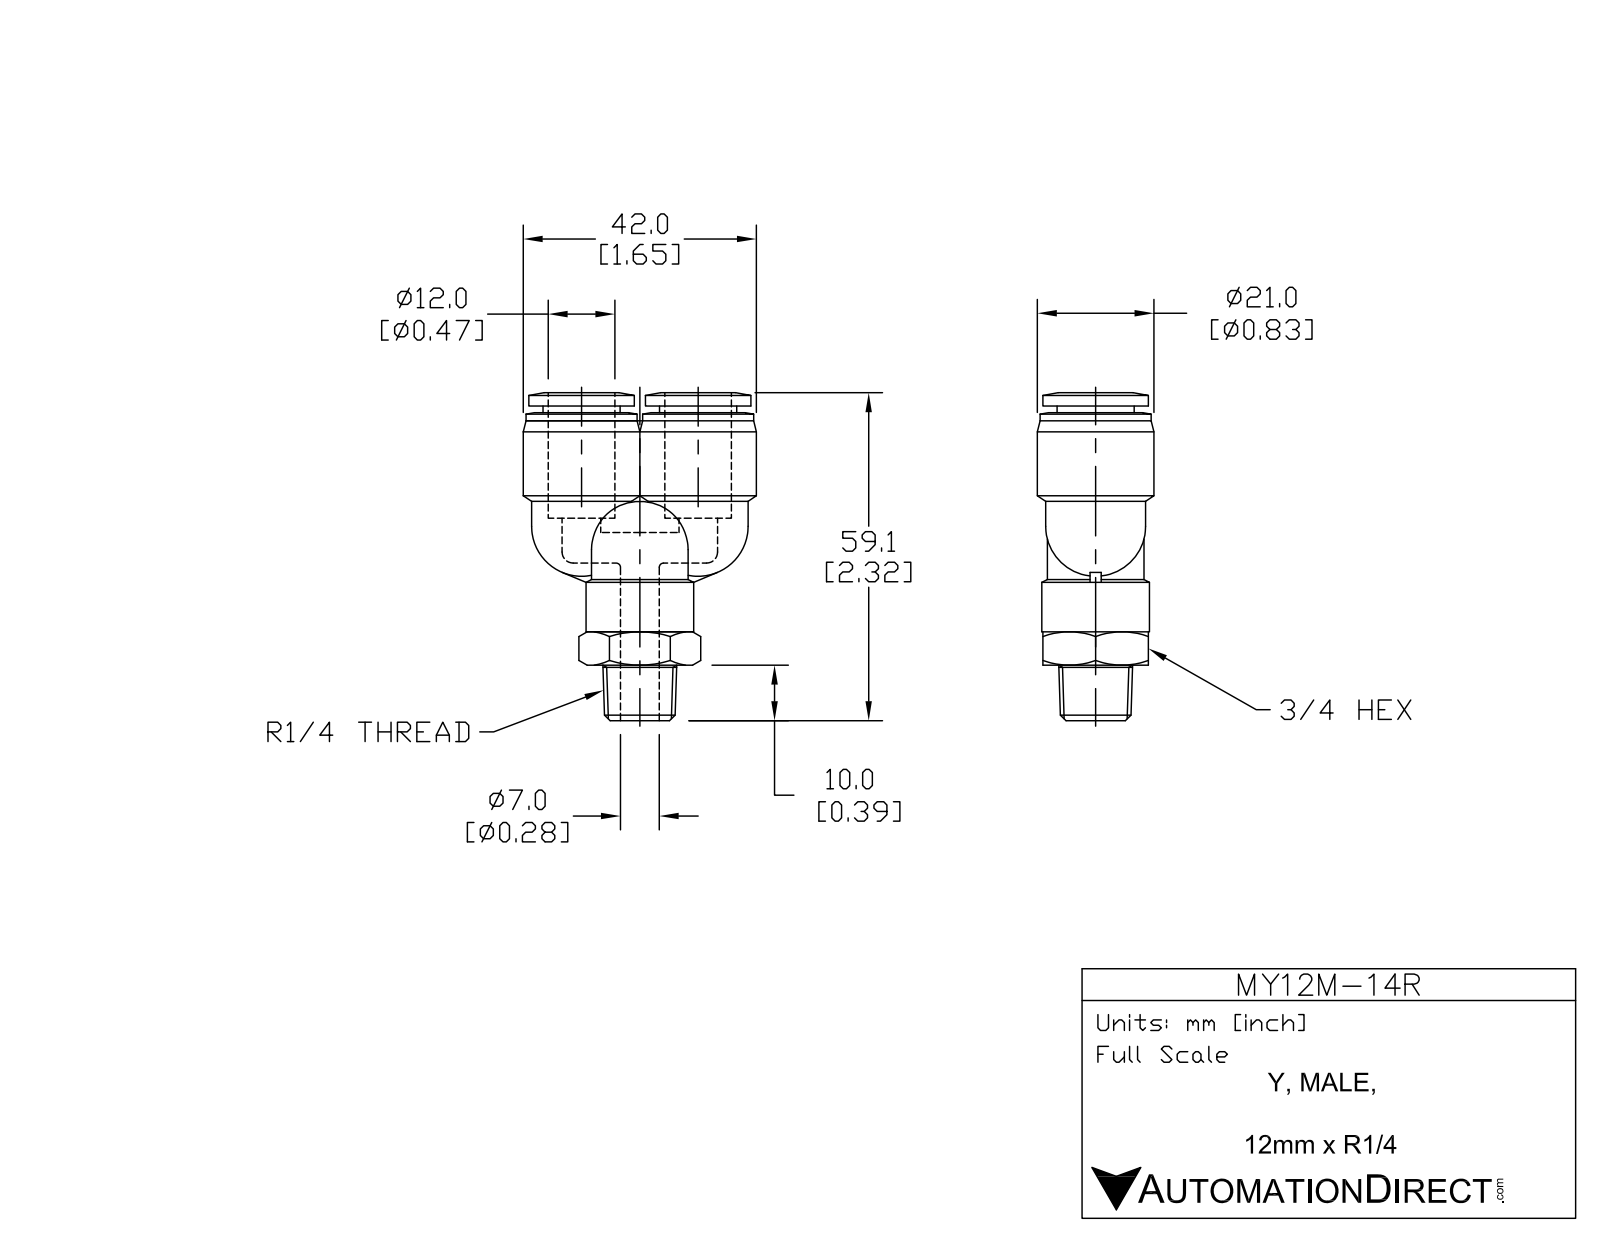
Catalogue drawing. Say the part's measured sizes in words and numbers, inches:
The part is named "MY12M-14R". Its 3-D file was written by "SolidWorks 2015 (AUTOMOTIVE_DESIGN)". It is 1 solid with 105 faces: 27 planar, 32 cylindrical and 46 other. Overall it measures 2.329 by 1.654 by 0.827 inches. Its volume is 1.036 cubic inches and its surface area 15.14 square inches. Round holes: 3 of diameter 0.354, 2 of diameter 0.484. Round bosses or shafts: 2 of diameter 0.827, 2 of diameter 0.787, 2 of diameter 0.748, 2 of diameter 0.709, 2 of diameter 0.547, 1 of diameter 0.764, 1 of diameter 0.685. The main face-to-face distances are 0.748, 0.799, 0.752, 0.047, 1.041, 1.793, 1.841, 0.394, 1.435, 2.187. The hole center spacings are 0.413, 0.827.
